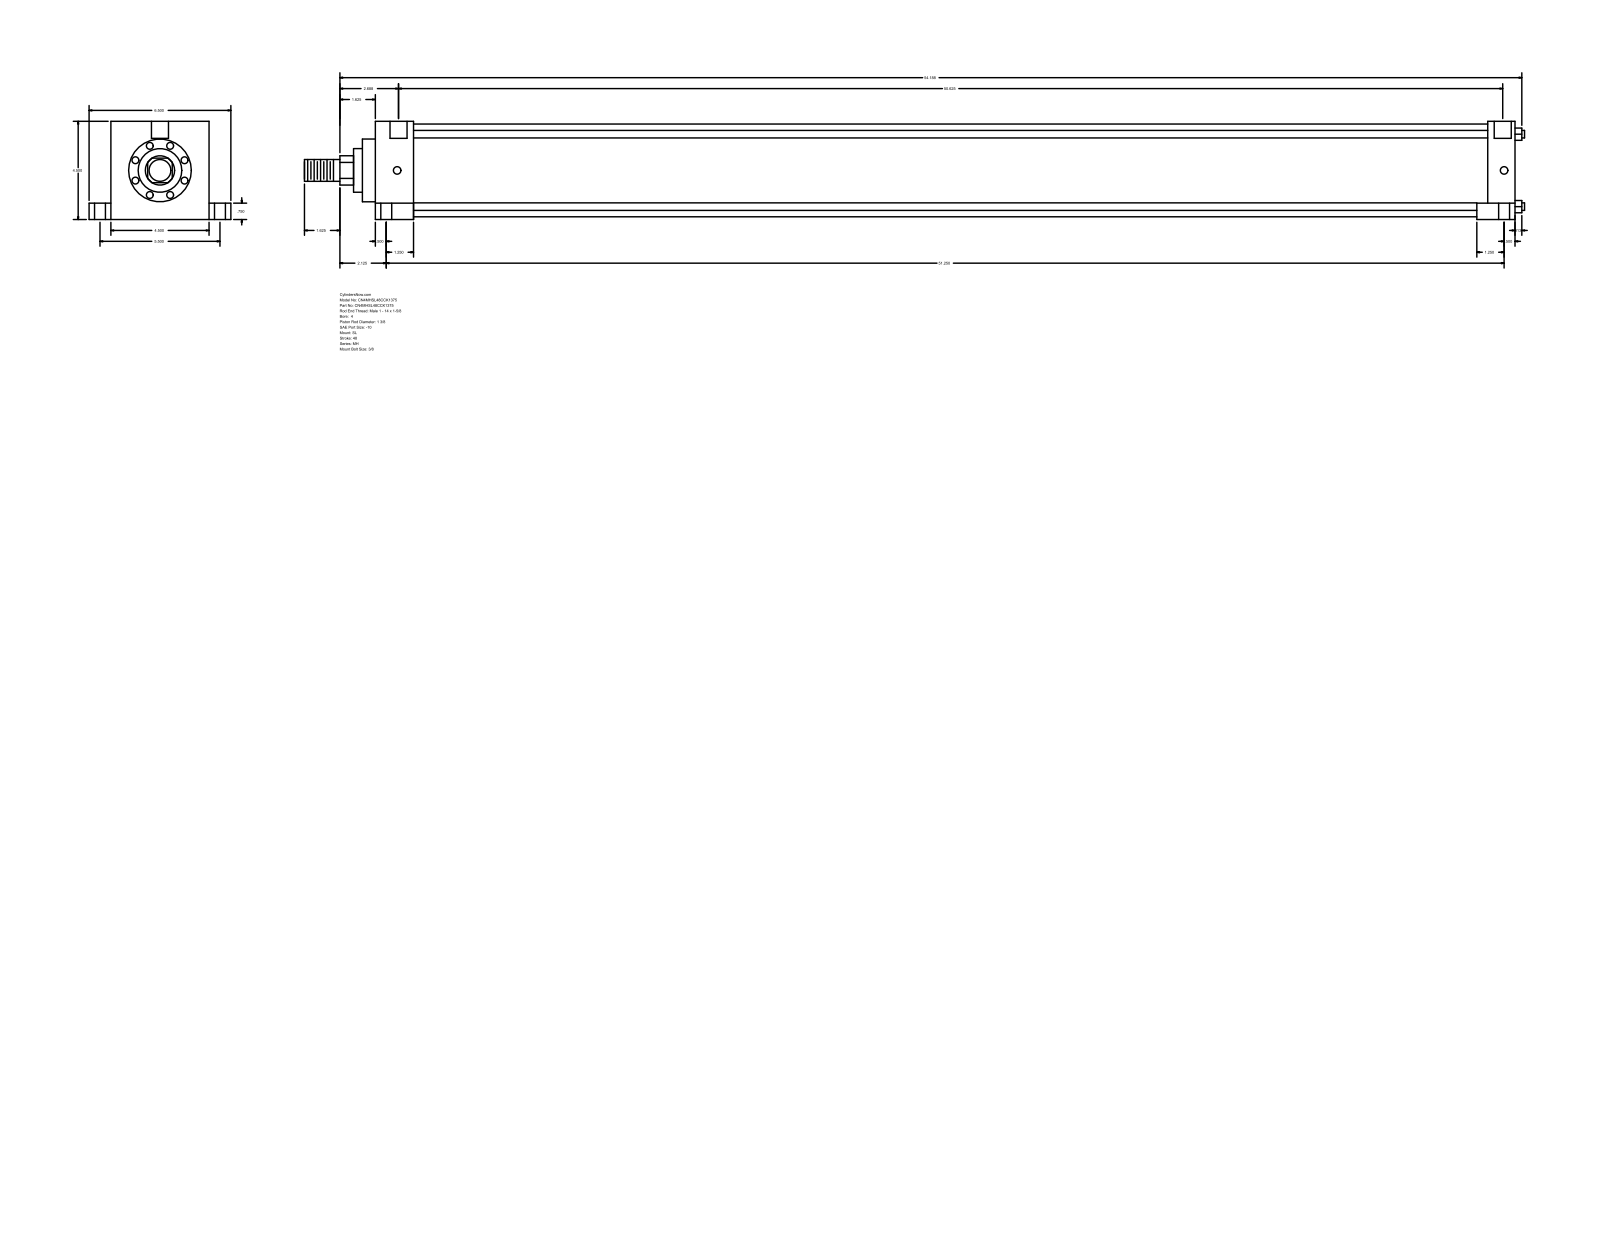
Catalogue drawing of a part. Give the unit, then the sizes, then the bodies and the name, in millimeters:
Units: millimetres
Overall size (bounding box): 1420.81 × 165.1 × 114.3
Round holes (diameter × count): ⌀8.73 ×4, ⌀12.7 ×4, ⌀19.05 ×4, ⌀19.84 ×2
Round bosses / shafts (diameter × count): ⌀8.76 ×4, ⌀107.95 ×1, ⌀73.03 ×1, ⌀50.8 ×1, ⌀34.92 ×1, ⌀25.4 ×1
Partial cylindrical surfaces — rounded edges, fillets, slot ends (radius × count): R17.06 ×1
Main face-to-face distances: 114.3, 1327.15, 44.45, 1282.7, 1295.4, 1250.95, 31.75, 25.4, 139.7, 19.05
Hole centre spacings: 69.85, 69.87, 70.99, 71.29, 139.7, 1289.05, 1289.35, 1290.94
Bodies: 0 solids, 110 faces (77 planar, 33 cylindrical, 0 other)
Part name (STEP PRODUCT): MH_SL__0400_1.375
STEP written by: GSSL Pune (CONFIG_CONTROL_DESIGN)
